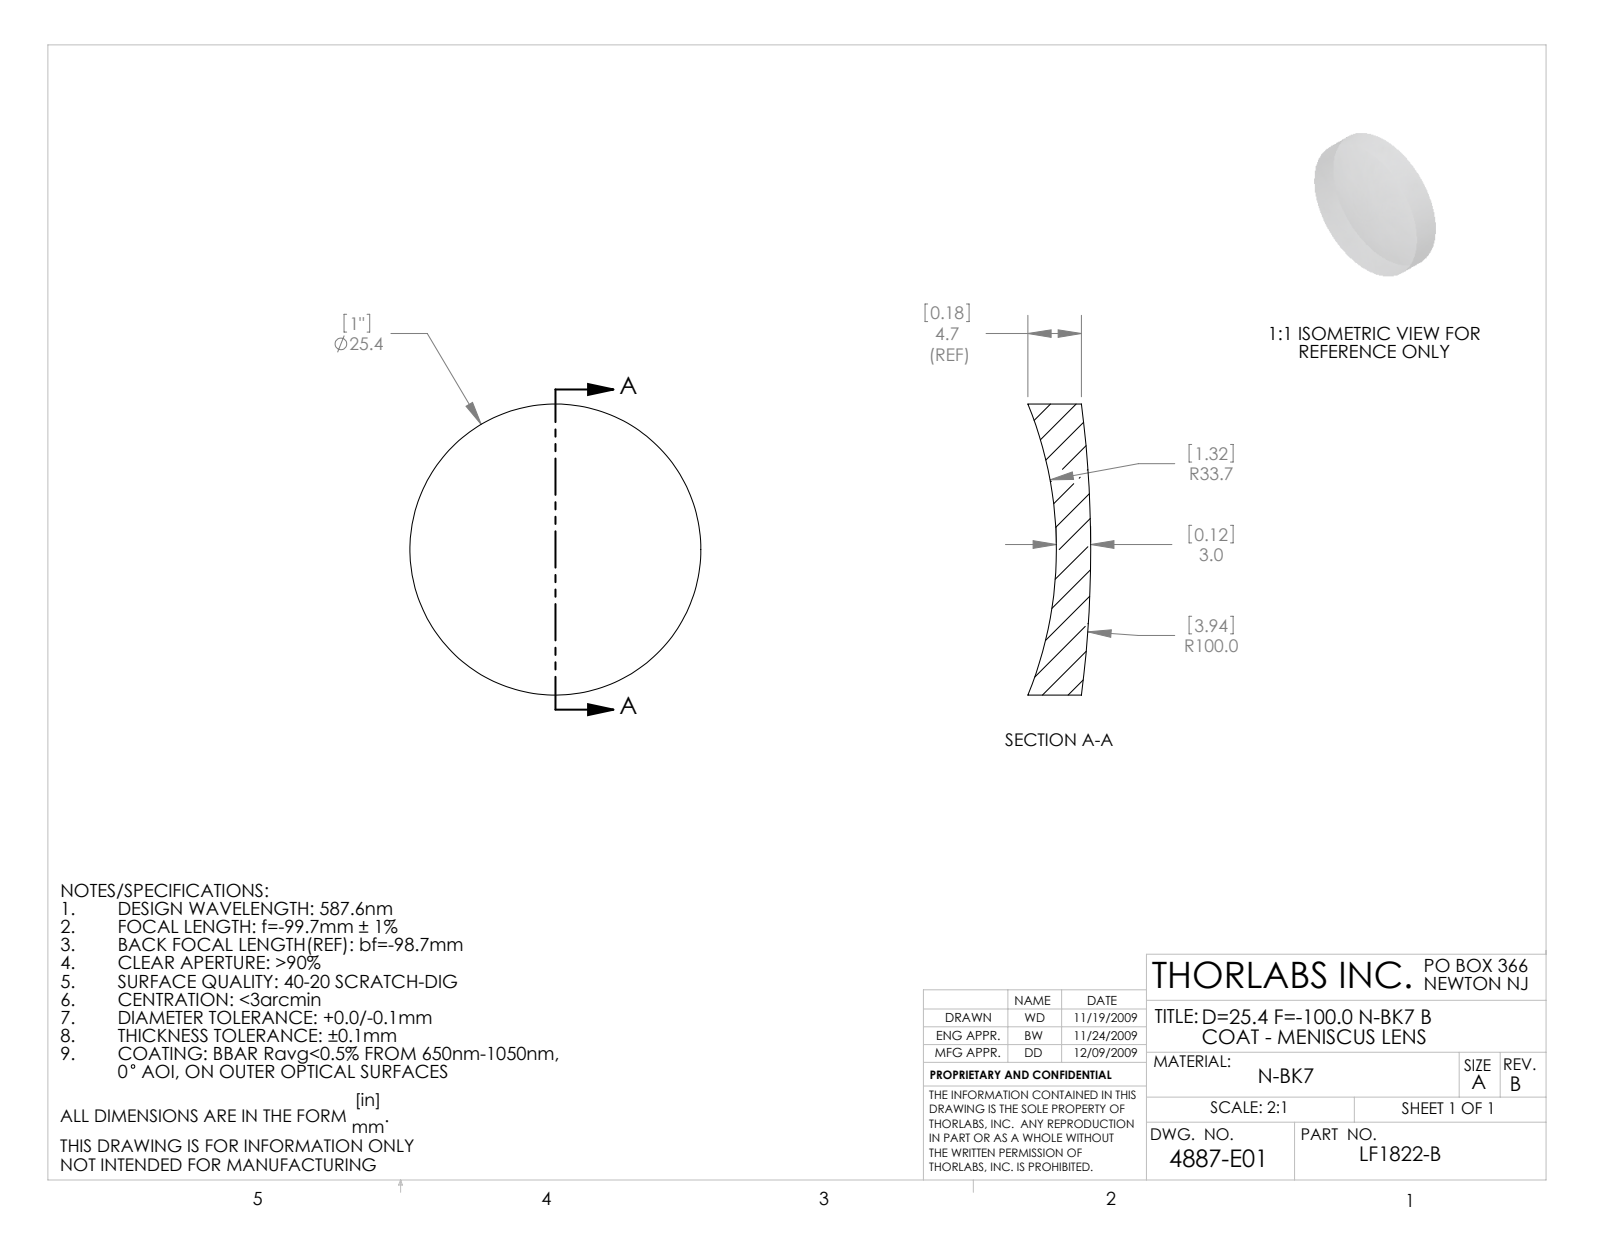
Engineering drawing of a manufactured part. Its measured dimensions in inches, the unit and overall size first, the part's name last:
Units: inches
Overall size (bounding box): 1 × 1 × 0.216
Round bosses / shafts (diameter × count): ⌀1 ×1
Volume: 0.118 in³ · Surface area: 2.182 in²
Bodies: 1 solid, 6 faces (0 planar, 2 cylindrical, 4 other)
Part name (STEP PRODUCT): 4887-E0W
STEP written by: SolidWorks 2009 (AUTOMOTIVE_DESIGN)
